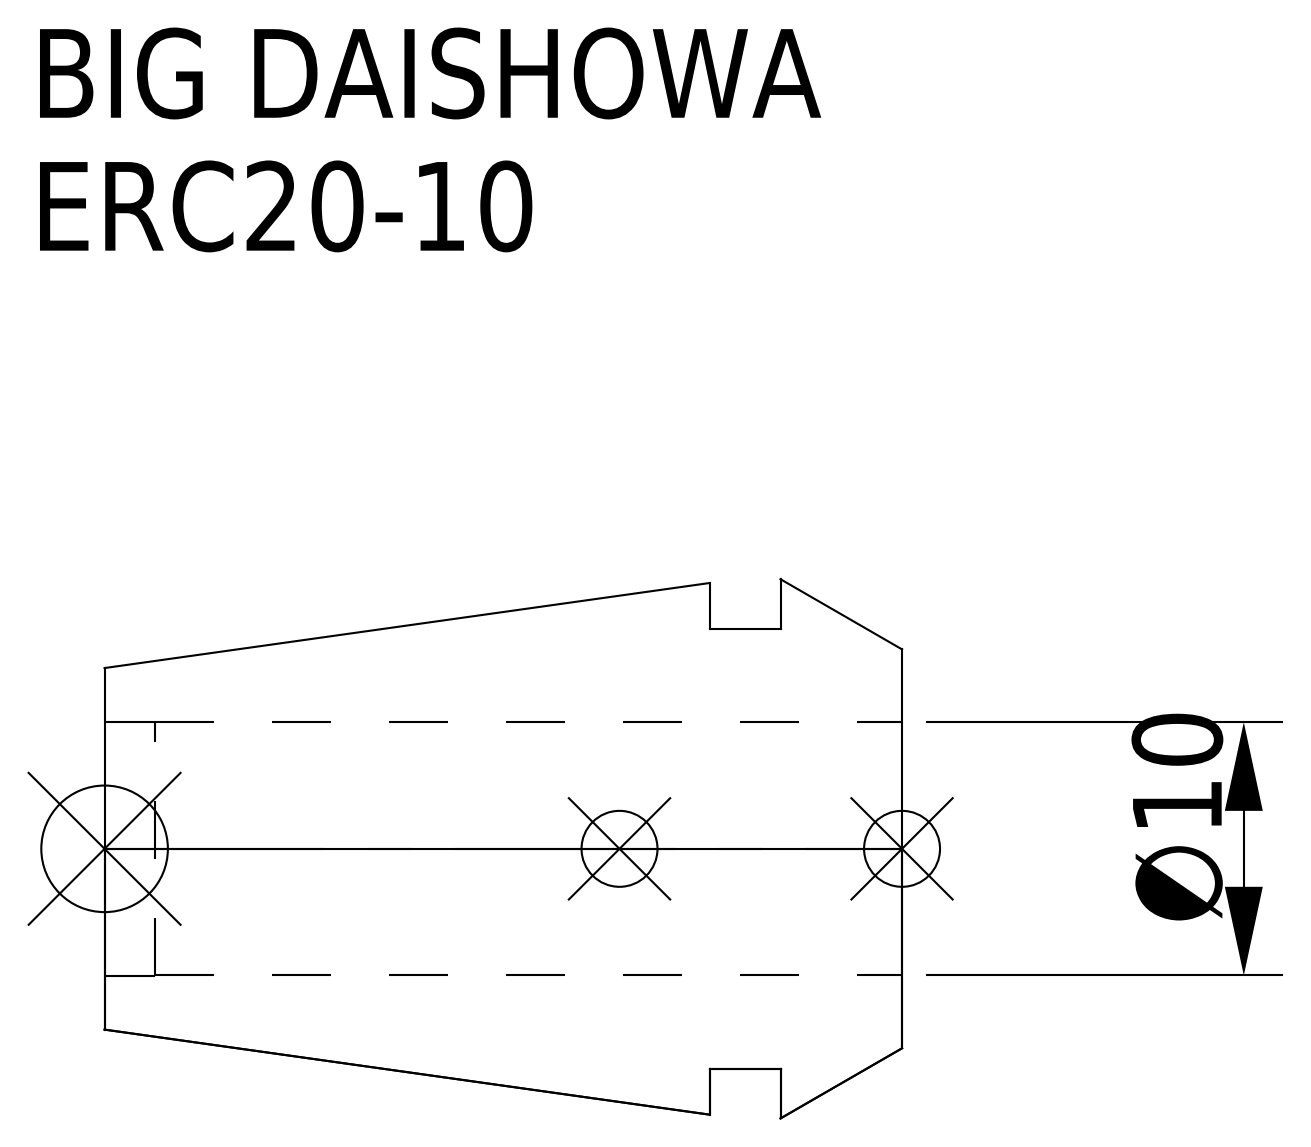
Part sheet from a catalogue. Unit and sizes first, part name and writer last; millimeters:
Units: millimetres
Overall size (bounding box): 31.5 × 21.3 × 21.3
Round holes (diameter × count): ⌀10 ×1, ⌀10.05 ×1
Round bosses / shafts (diameter × count): ⌀17.4 ×1
Main face-to-face distances: 4.8, 7.6, 2.8, 31.5, 26.7, 23.9, 29.5, 24.7, 21.9, 2
Volume: 5 407 mm³ · Surface area: 3 229 mm²
Bodies: 1 solid, 15 faces (5 planar, 6 cylindrical, 4 other)
Part name (STEP PRODUCT): ERC20-10
STEP written by: CREO PARAMETRIC BY PTC INC, 2016380 (AUTOMOTIVE_DESIGN)
